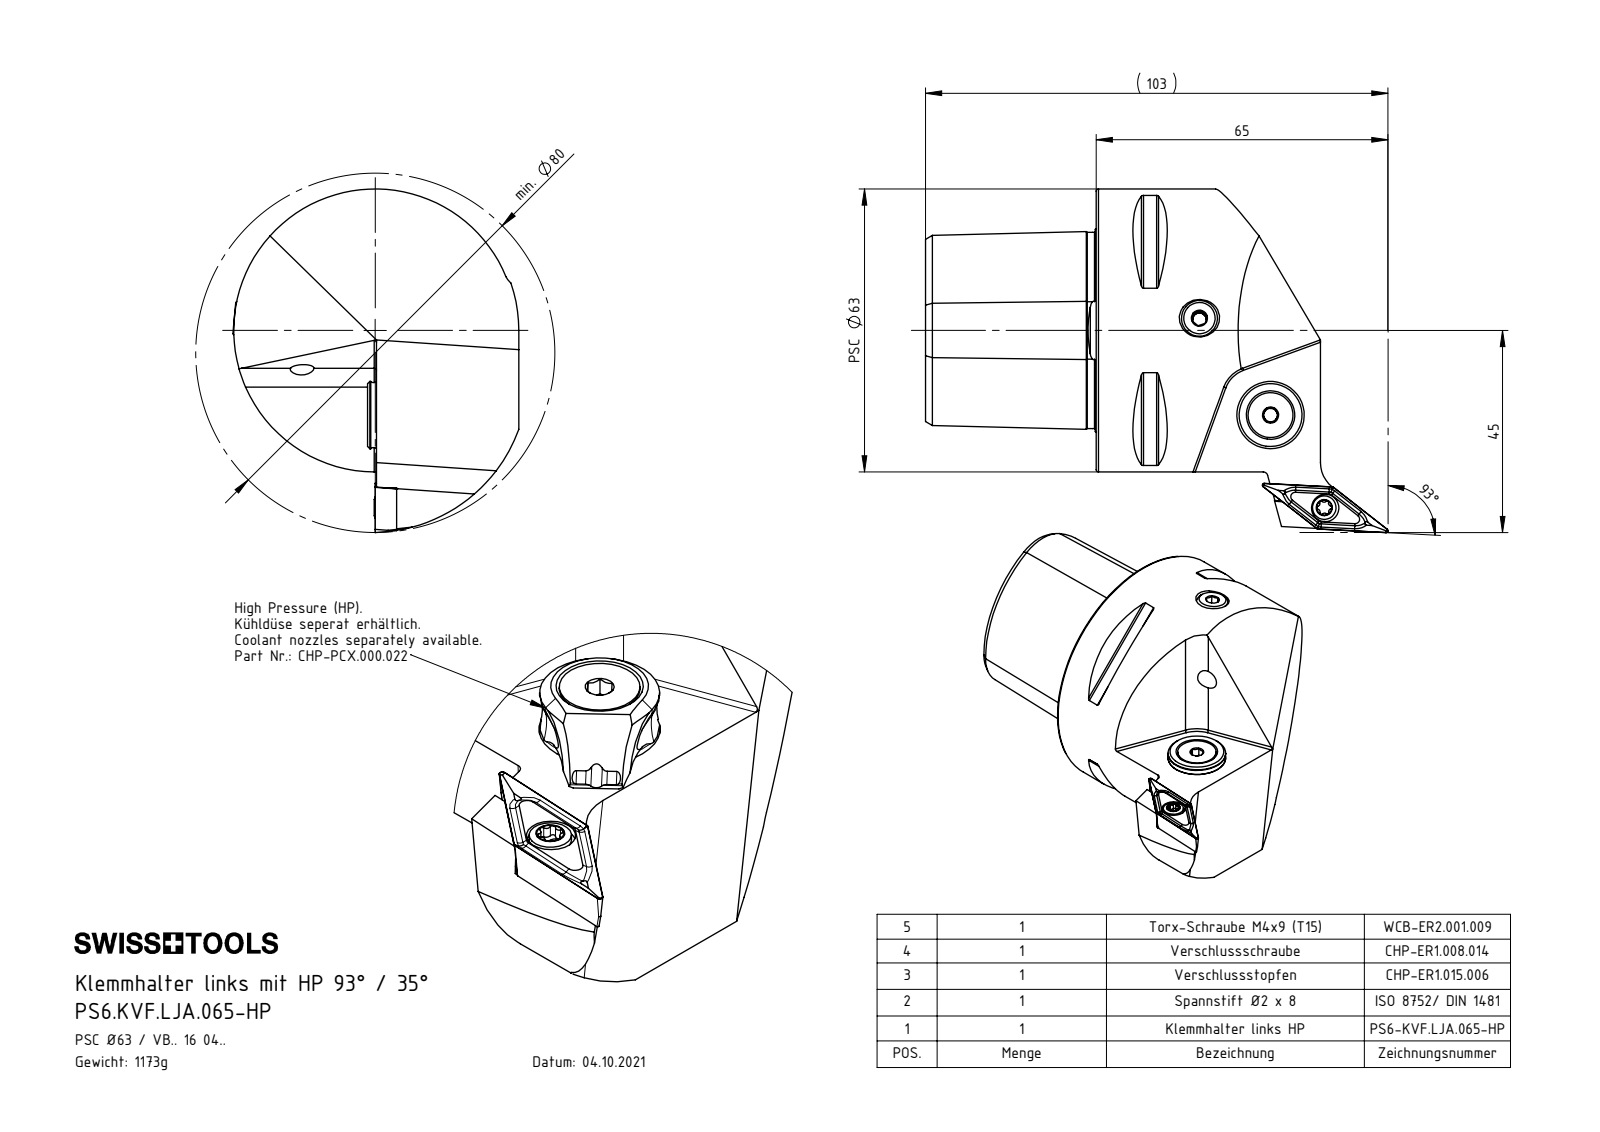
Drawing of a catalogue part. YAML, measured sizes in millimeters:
part_name: "WCB-ER2.001.009_A; VBMT160404; DIN 3771 - 13x1; ISO 8752 2x8 (+7 more)"
step_written_by: "SolidWorks 2022 (CONFIG_CONTROL_DESIGN)"
units: millimeters
bodies: {solids: 9, faces: 483, planar: 107, cylindrical: 134, other: 242}
overall_size: [103, 76.5, 63.5]
volume: 149423
surface_area: 30972
round_holes:
  - {diameter: 4.2, count: 2}
  - {diameter: 5, count: 2}
  - {diameter: 1.2, count: 1}
  - {diameter: 2, count: 1}
  - {diameter: 3, count: 1}
  - {diameter: 3.3, count: 1}
  - {diameter: 4.4, count: 1}
  - {diameter: 5.3, count: 1}
  - {diameter: 6.1, count: 1}
  - {diameter: 7, count: 1}
  - {diameter: 8.1, count: 1}
  - {diameter: 10, count: 1}
round_bosses_or_shafts:
  - {diameter: 63, count: 1}
  - {diameter: 14.85, count: 1}
  - {diameter: 13.4, count: 1}
  - {diameter: 10, count: 1}
  - {diameter: 8, count: 1}
  - {diameter: 5.5, count: 1}
  - {diameter: 5.25, count: 1}
  - {diameter: 5, count: 1}
partial_cylinders:
  - {radius: 0.5, count: 12}
  - {radius: 1, count: 7}
  - {radius: 0.34, count: 6}
  - {radius: 0.59, count: 6}
  - {radius: 6, count: 4}
  - {radius: 0.15, count: 2}
  - {radius: 1.1, count: 2}
  - {radius: 1.2, count: 2}
face_to_face_distances: [38, 24.88, 11, 27, 4.46, 27.24, 31.7, 55.8, 27.2, 4.5]
hole_center_spacings: [4.49, 21.35, 21.49, 23.83, 24, 27.5, 32.79, 36.85]
